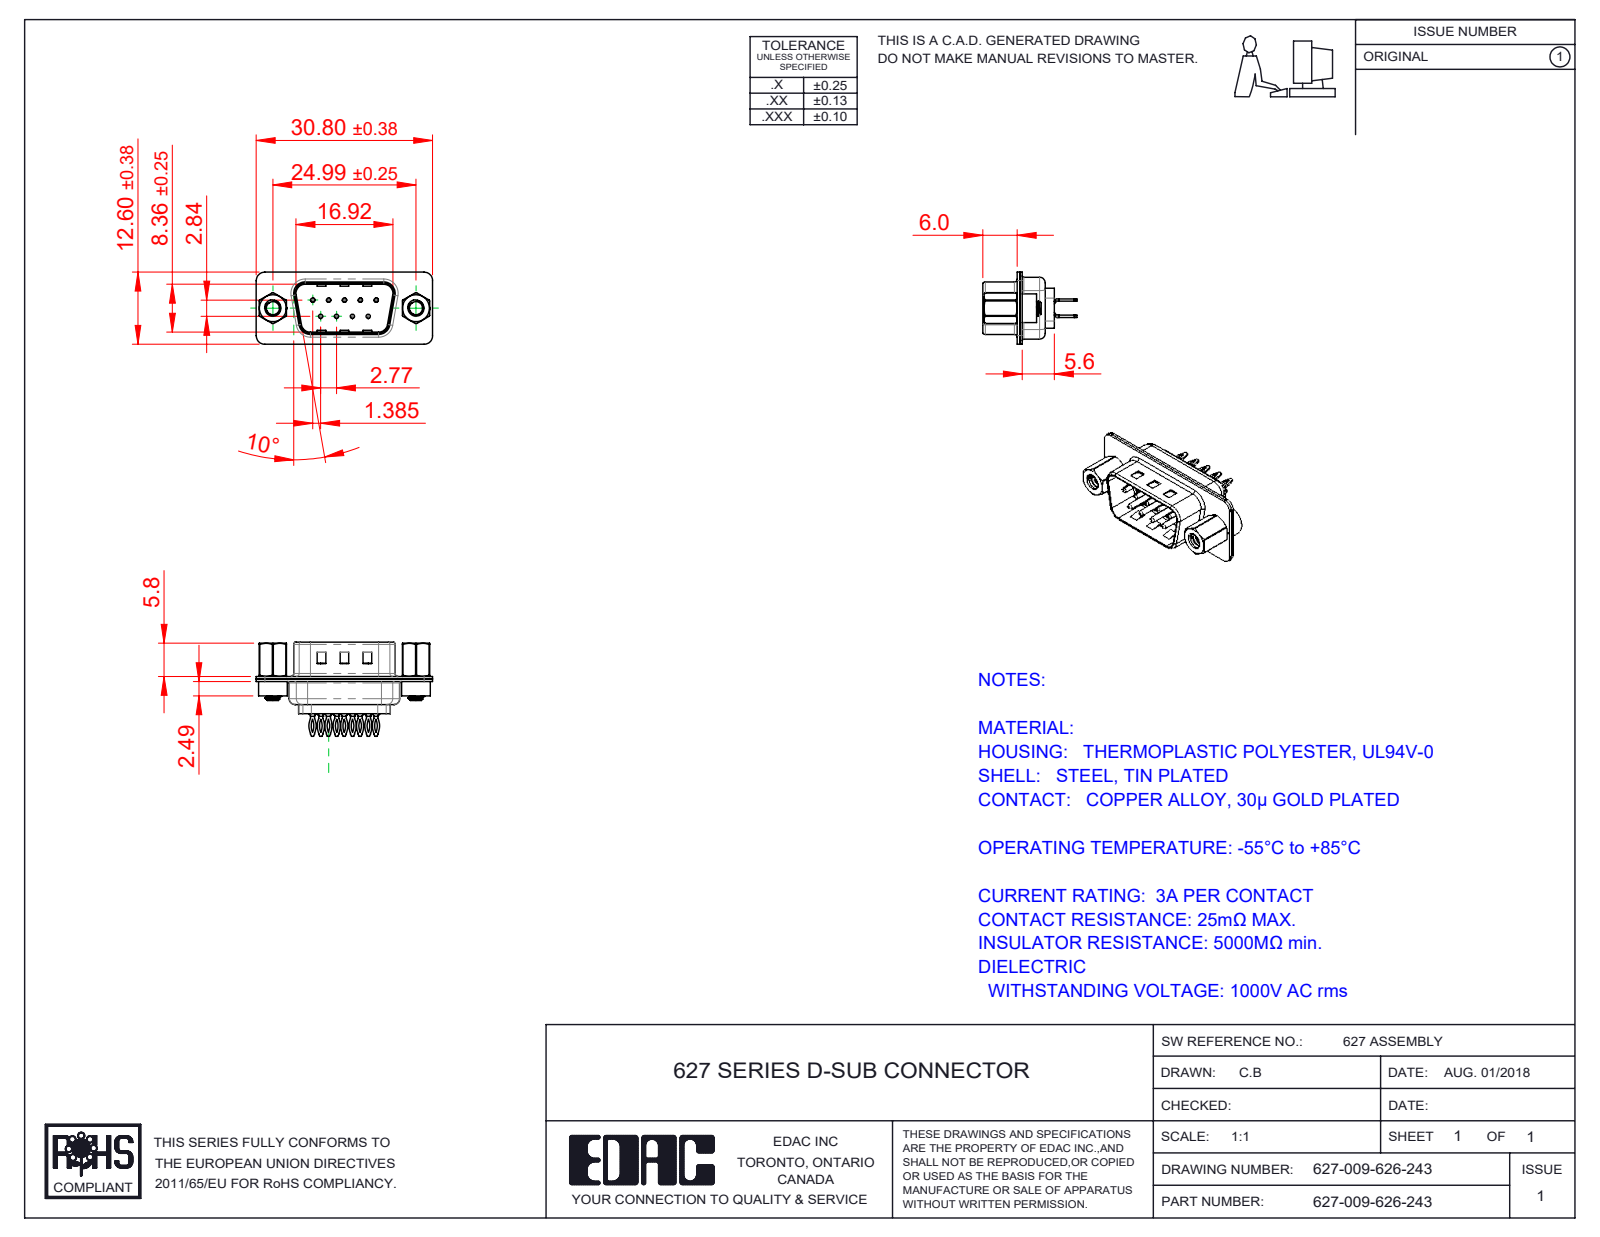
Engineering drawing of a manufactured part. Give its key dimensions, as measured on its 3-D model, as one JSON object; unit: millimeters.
{"part_name": "627 Shell Front_09 Contacts; 627 Contact Row 2_26L; 627 4-40 Threaded Rivet; 627 Shell Rear_09 Contacts (+4 more)", "step_written_by": "SolidWorks 2020 (CONFIG_CONTROL_DESIGN)", "units": "millimeters", "bodies": {"solids": 16, "faces": 1110, "planar": 309, "cylindrical": 478, "other": 323}, "overall_size": [30.8, 16.45, 12.6], "volume_mm3": 1519, "surface_area_mm2": 4378, "round_holes": [[0.35, 9], [1.1, 9], [1.6, 9], [2.26, 2], [2.29, 2], [4, 2], [4.8, 2]], "round_bosses_or_shafts": [[2, 9], [1.5, 9], [0.75, 9], [5, 2], [4.9, 2], [2.79, 2]], "partial_cylinders_radius": [[1.5, 18], [2.92, 18], [3.33, 18], [2, 12], [0.5, 8], [1.6, 8], [0.25, 4], [0.6, 4]], "face_to_face_distances": [0.45, 0.4, 0.9, 0.82, 9.58, 1.4, 8.76, 0.5, 1.5, 6.05], "hole_center_spacings": [3.16, 2.77, 5.54, 5.03, 5.04, 8.31, 7.48, 7.49]}
